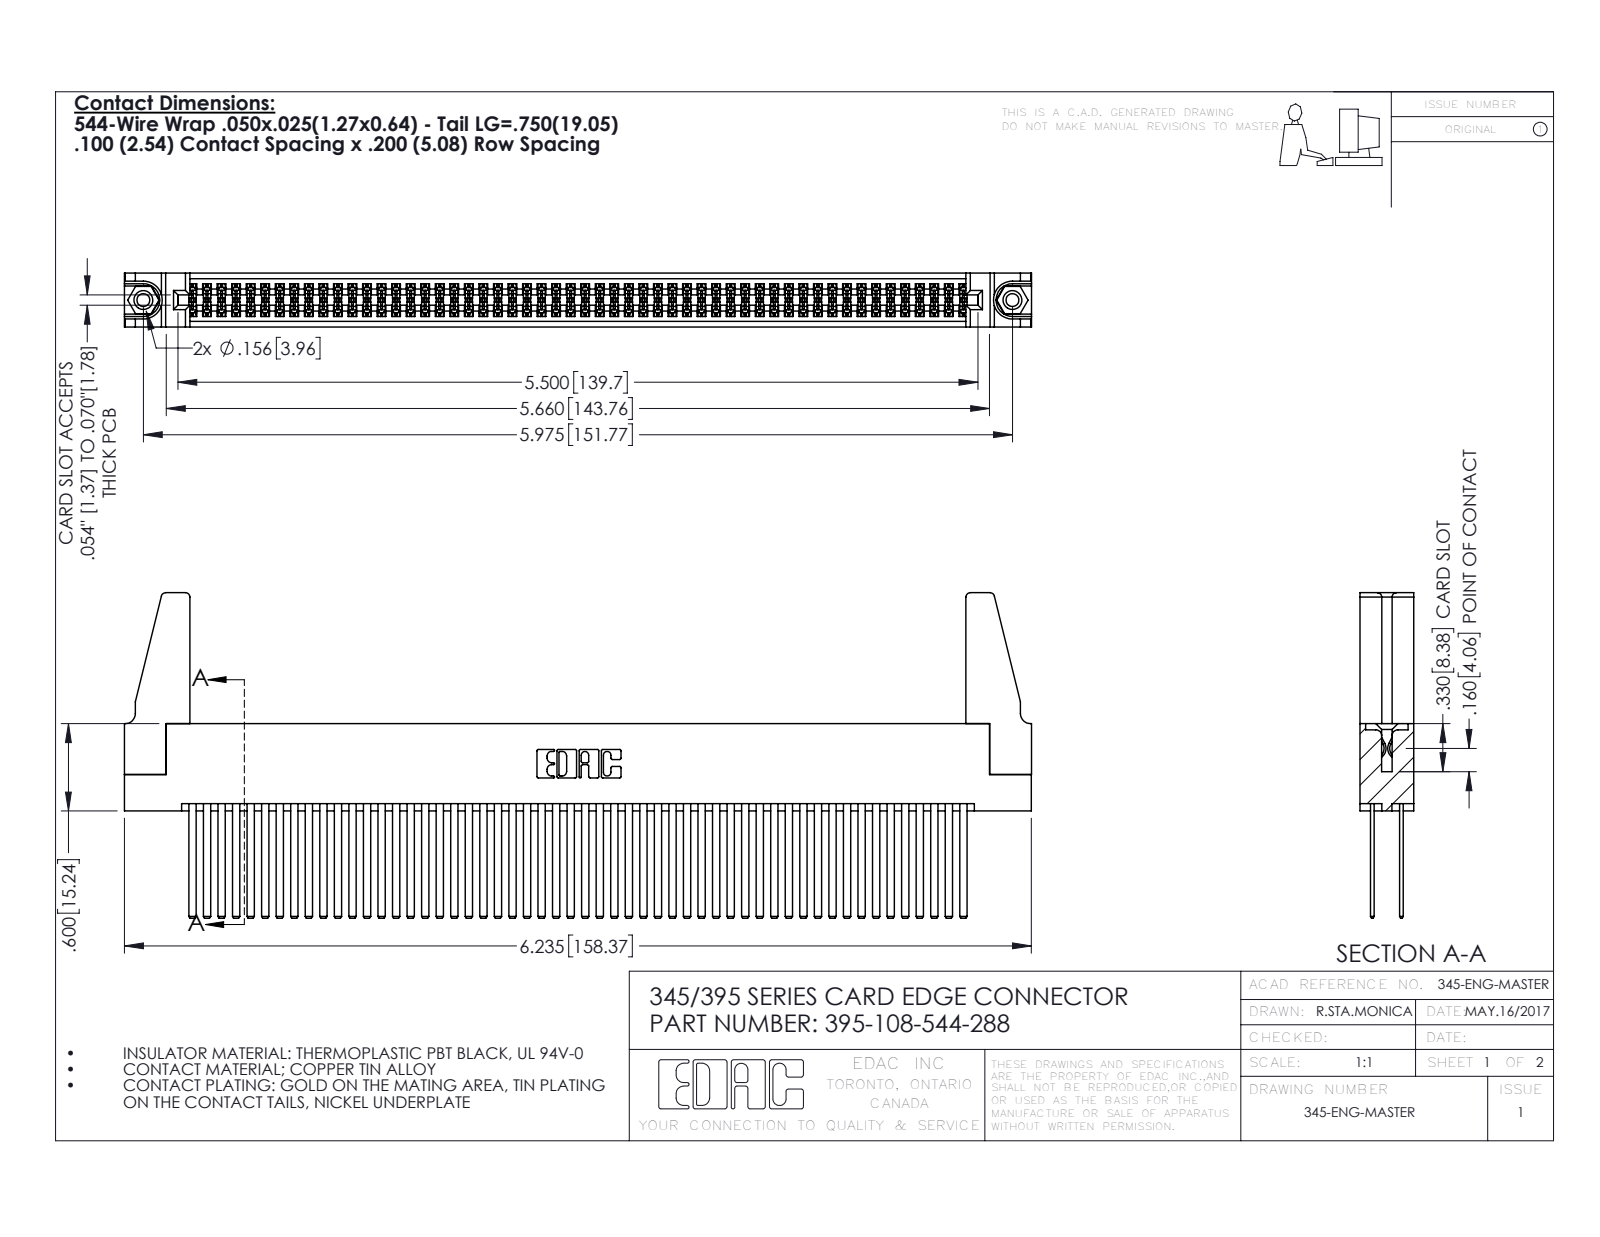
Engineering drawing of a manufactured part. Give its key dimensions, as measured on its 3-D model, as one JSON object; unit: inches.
{"part_name": "345-250-001_345-250-001-102; 345-292-001_345-293-144; 345 Part_Flush Mounting Lugs - 0.156 Dia-TH; 345-220-078_345-220-088 (+1 more)", "step_written_by": "SolidWorks 2016 (CONFIG_CONTROL_DESIGN)", "units": "inches", "bodies": {"solids": 113, "faces": 5002, "planar": 3284, "cylindrical": 1702, "other": 16}, "overall_size": [6.236, 2.237, 0.37], "volume_in3": 1.237, "surface_area_in2": 51.05, "round_holes": [[0.089, 2], [0.125, 2], [0.156, 2], [0.064, 1]], "round_bosses_or_shafts": [[0.155, 2]], "partial_cylinders_radius": [[0.006, 162], [0.01, 22], [0.03, 8], [0.007, 6], [0.031, 6], [0.026, 3], [0.014, 2], [0.019, 2]], "face_to_face_distances": [0.072, 0.298, 0.2, 0.098, 0.272, 0.025, 0.225, 0.37, 0.175, 0.149], "hole_center_spacings": [0.27, 5.739, 5.975]}
